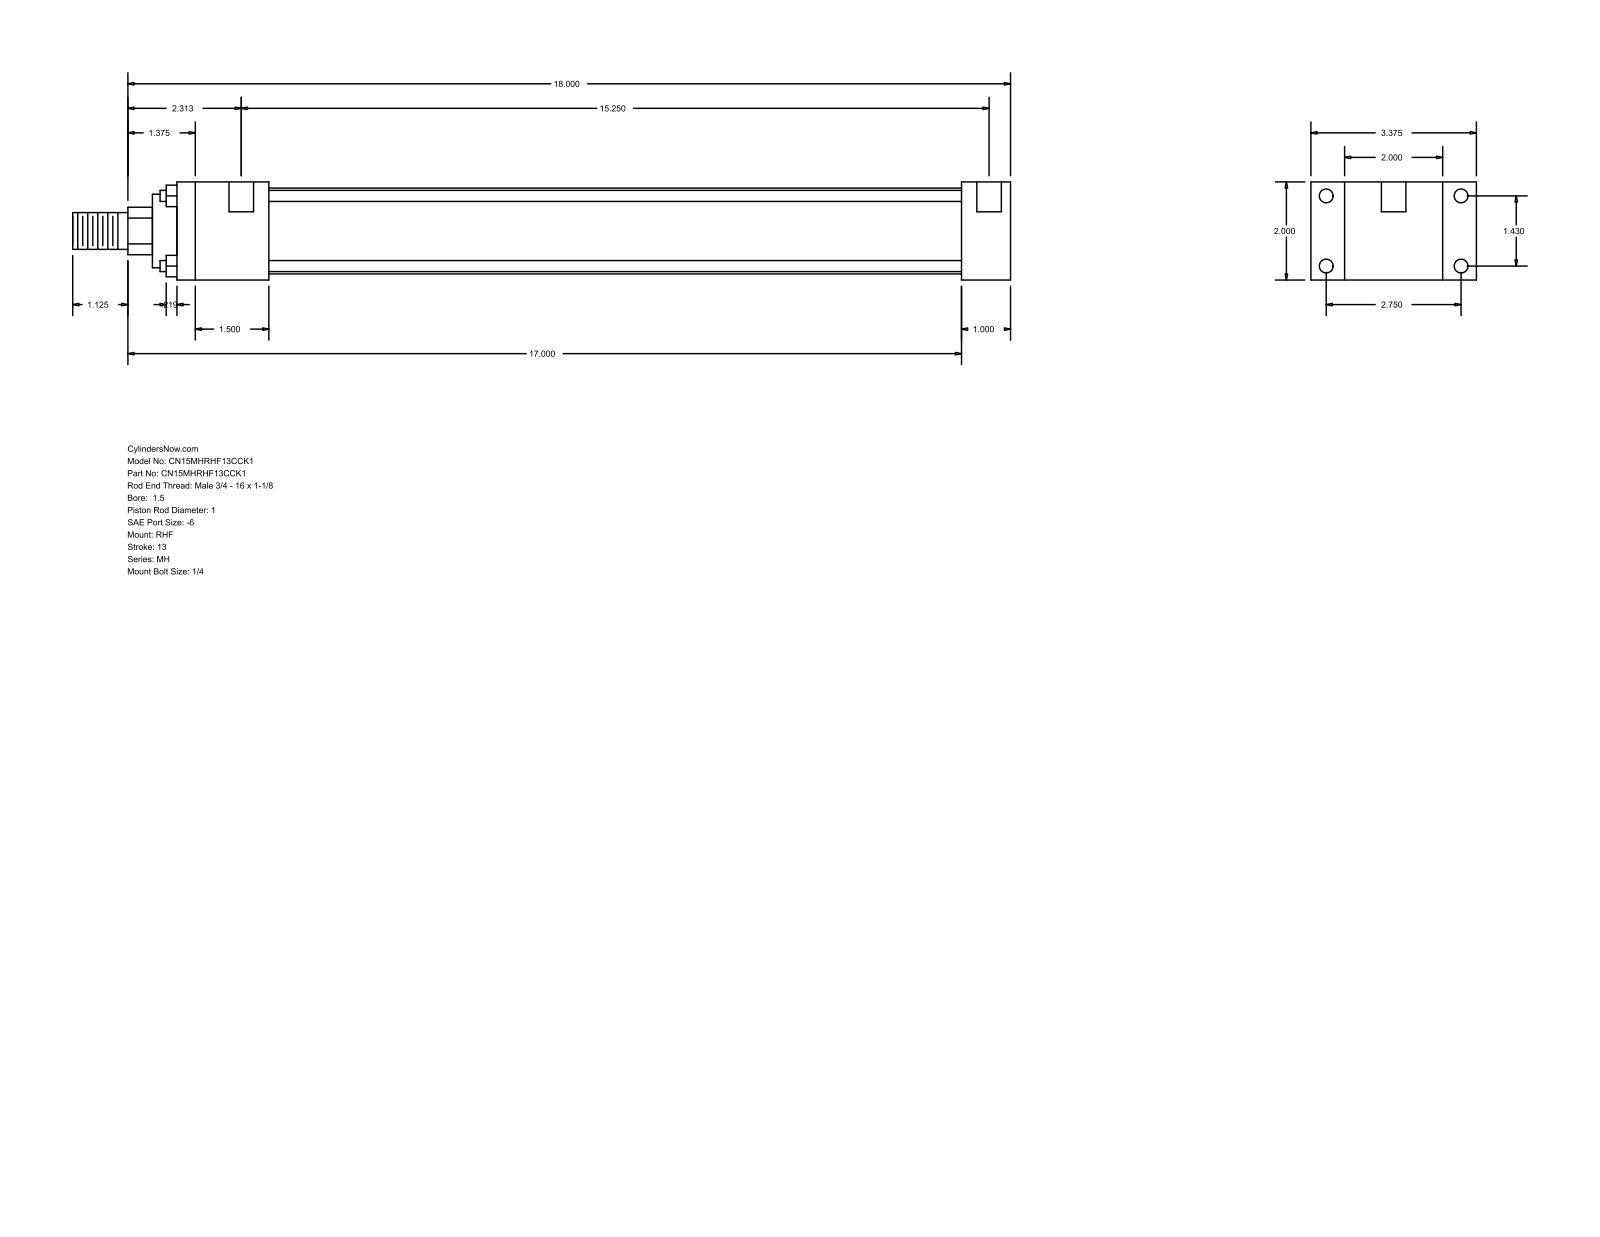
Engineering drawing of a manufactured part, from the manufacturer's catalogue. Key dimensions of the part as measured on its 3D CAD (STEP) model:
Part name (STEP PRODUCT): MH_RHF__0150_1
STEP written by: GSSL Pune (CONFIG_CONTROL_DESIGN)
Units: millimetres
Bodies: 0 solids, 88 faces (60 planar, 28 cylindrical, 0 other)
Overall size (bounding box): 485.77 × 85.72 × 50.8
Round holes (diameter × count): ⌀5.56 ×4, ⌀7.14 ×4, ⌀12.7 ×2
Round bosses / shafts (diameter × count): ⌀5.71 ×4, ⌀44.45 ×1, ⌀38.1 ×1, ⌀25.4 ×1, ⌀19.05 ×1
Partial cylindrical surfaces — rounded edges, fillets, slot ends (radius × count): R12.29 ×1
Main face-to-face distances: 50.8, 25.4, 17.46, 68.26, 85.72, 431.8, 406.4, 47.63, 358.77, 384.17
Hole centre spacings: 36.32, 69.84, 78.72, 390.53, 3.18, 387.35
